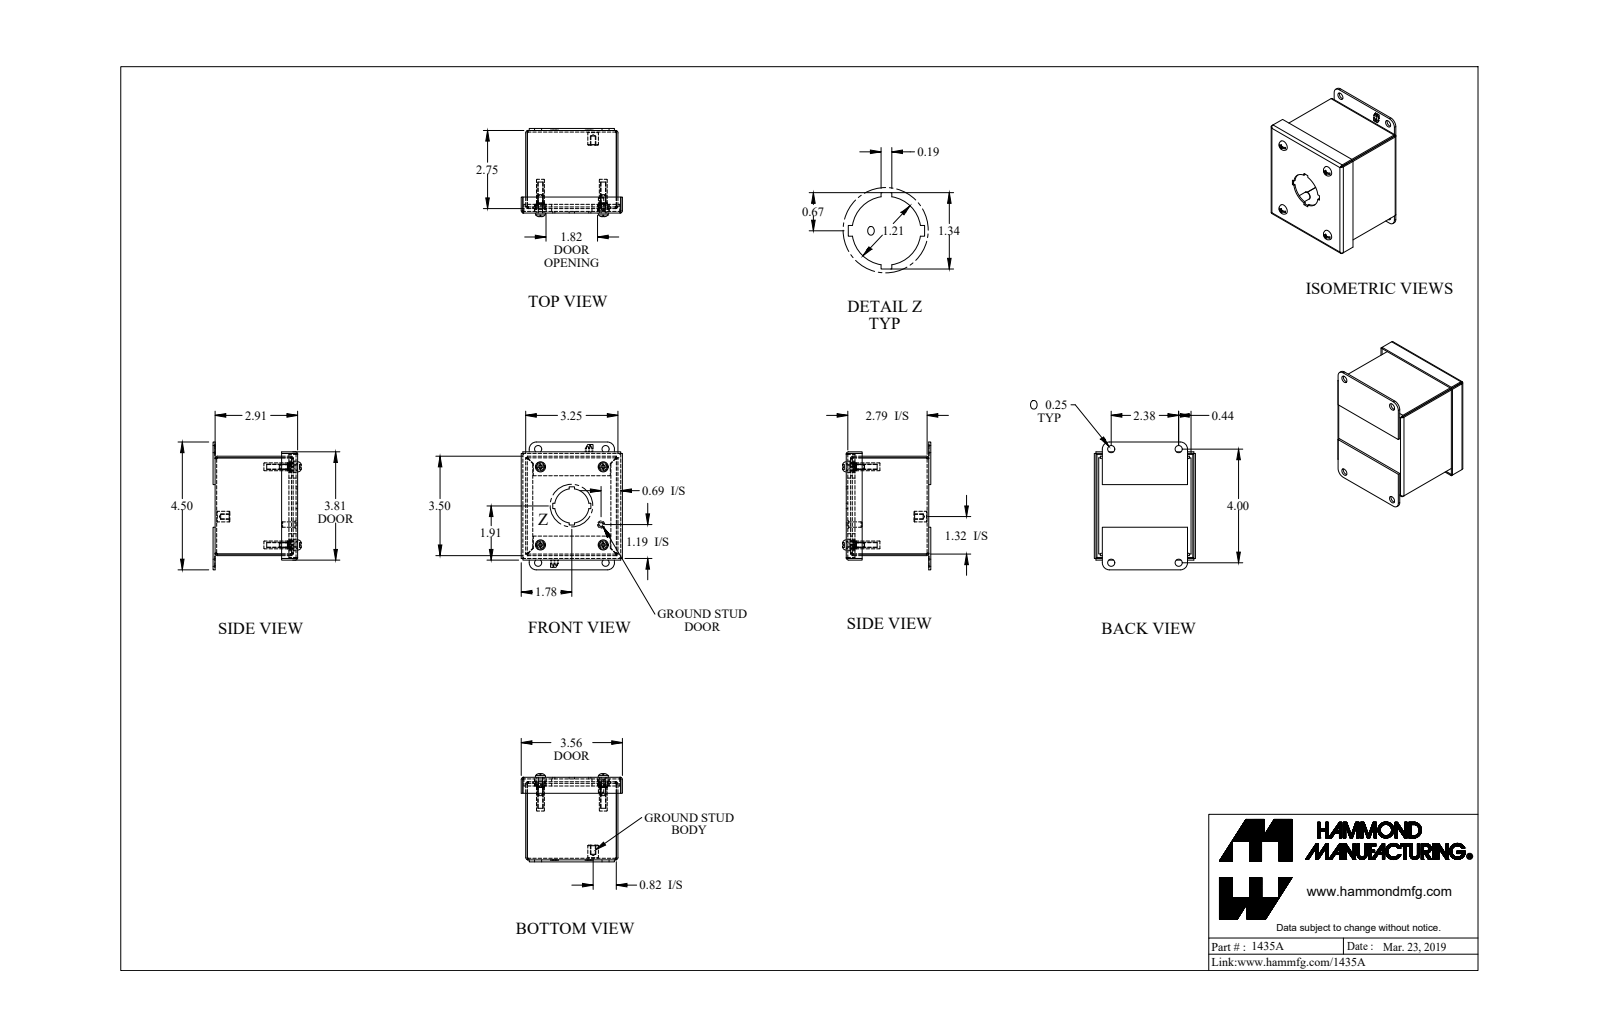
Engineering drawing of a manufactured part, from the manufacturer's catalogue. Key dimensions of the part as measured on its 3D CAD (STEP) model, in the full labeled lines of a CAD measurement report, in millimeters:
Part name (STEP PRODUCT): 1435A_Default
STEP written by: SolidWorks 2019 (CONFIG_CONTROL_DESIGN)
Units: millimetres
Bodies: 19 solids, 571 faces (371 planar, 144 cylindrical, 56 other)
Overall size (bounding box): 114.3 × 90.5 × 78.9
Volume: 101 900 mm³ · Surface area: 123 200 mm²
Round holes (diameter × count): ⌀6.4 ×8, ⌀4 ×4, ⌀10.3 ×4, ⌀4 ×1, ⌀30.7 ×1
Round bosses / shafts (diameter × count): ⌀9.9 ×4, ⌀7 ×4, ⌀4.8 ×4, ⌀3.8 ×4, ⌀9.5 ×1, ⌀6.4 ×1, ⌀4.8 ×1
Partial cylindrical surfaces — rounded edges, fillets, slot ends (radius × count): R0.7 ×12, R2.2 ×12, R4.1 ×4, R4.3 ×4, R6.4 ×4
Main face-to-face distances: 1.4, 72.4, 1.4, 81.1, 87.5, 73.8, 70.9, 4, 75.7, 74.2
Hole centre spacings: 69.9, 16, 44.8, 56.1, 56.2, 59.1, 85.8, 103.6
